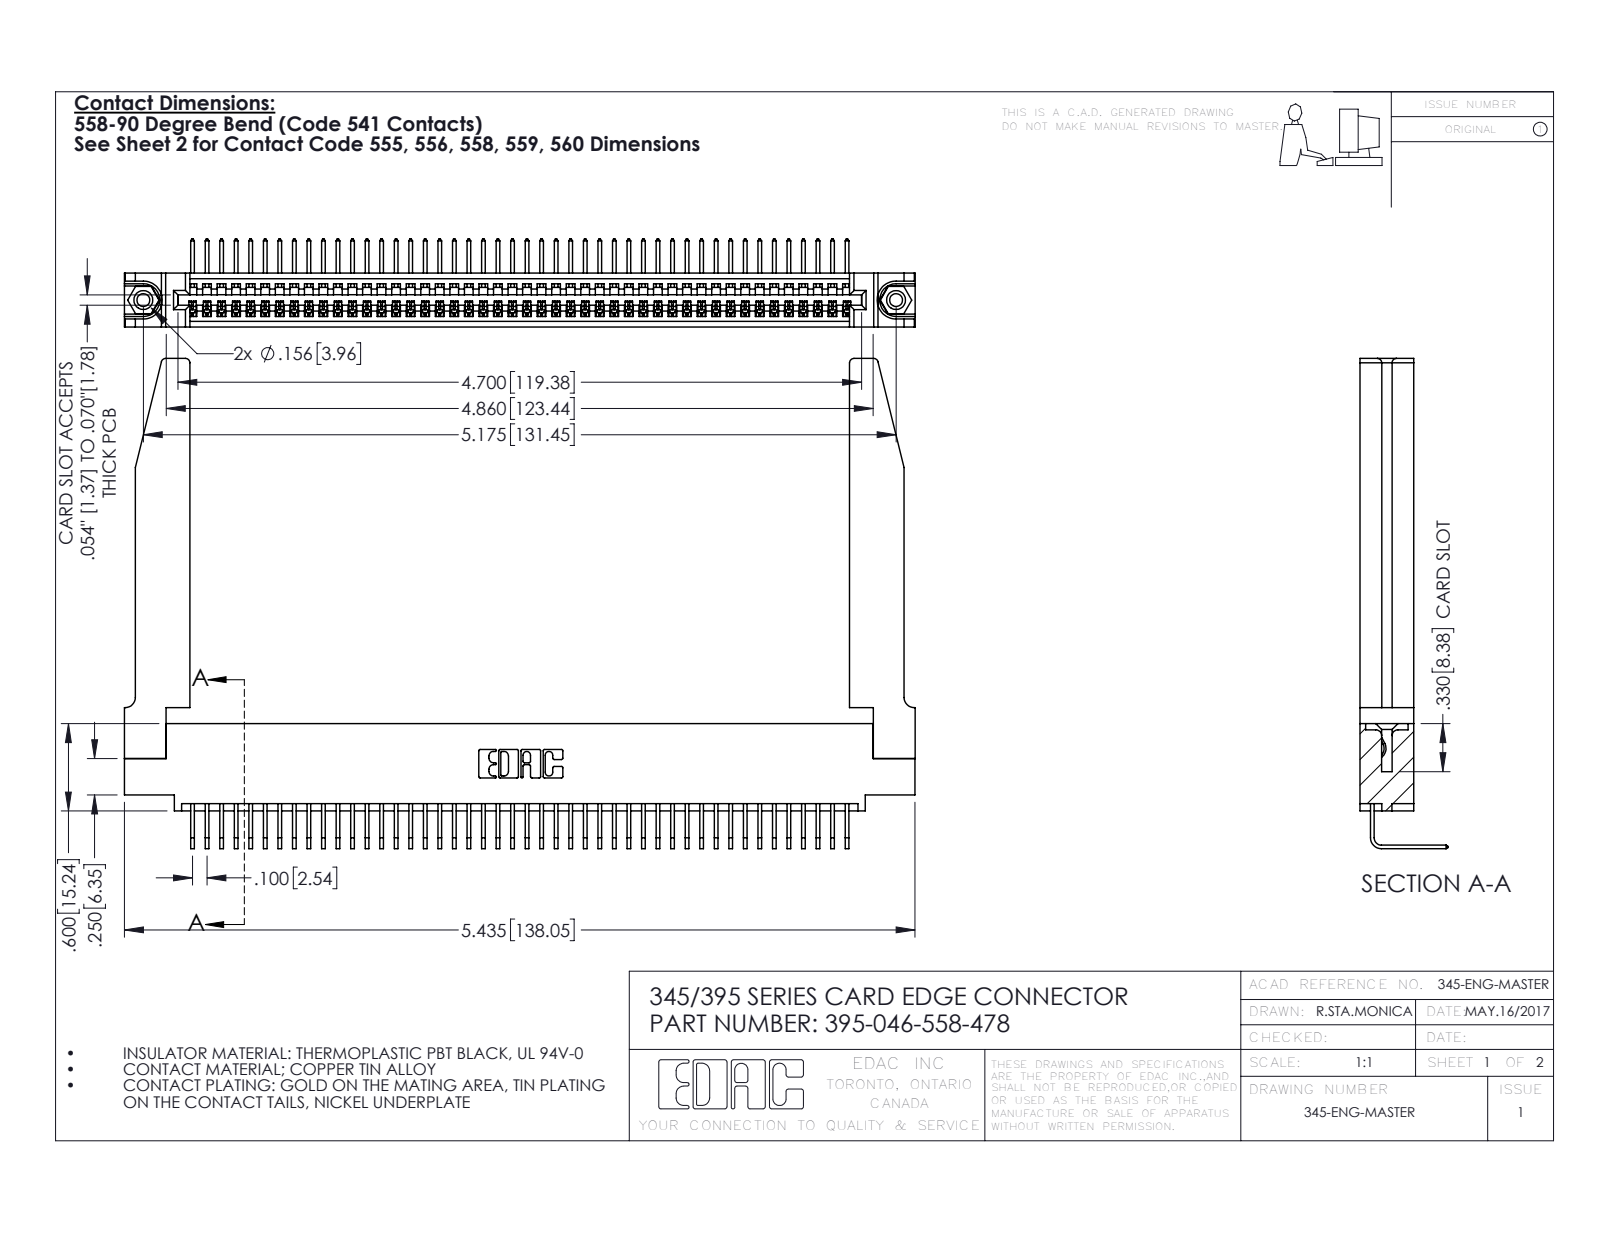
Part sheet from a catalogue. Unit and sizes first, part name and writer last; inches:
Units: inches
Overall size (bounding box): 5.436 × 3.369 × 0.605
Round holes (diameter × count): ⌀0.089 ×2, ⌀0.125 ×2, ⌀0.156 ×2, ⌀0.064 ×1
Round bosses / shafts (diameter × count): ⌀0.155 ×2
Partial cylindrical surfaces — rounded edges, fillets, slot ends (radius × count): R0.006 ×92, R0.01 ×22, R0.03 ×8, R0.007 ×6, R0.031 ×6, R0.026 ×3, R0.031 ×2, R0.04 ×2
Main face-to-face distances: 0.37, 0.072, 0.298, 0.2, 0.098, 0.272, 0.025, 0.225, 0.148, 0.15
Hole centre spacings: 0.27, 4.939, 5.175
Volume: 1.281 in³ · Surface area: 39.46 in²
Bodies: 51 solids, 3124 faces (2158 planar, 914 cylindrical, 52 other)
Part name (STEP PRODUCT): 345-250-001_345-250-001-102; 345-220-078_345-220-078; 345 Part_0.110 Offset - 0.156 Dia-TH; 395-046-558-478 (+1 more)
STEP written by: SolidWorks 2016 (CONFIG_CONTROL_DESIGN)
